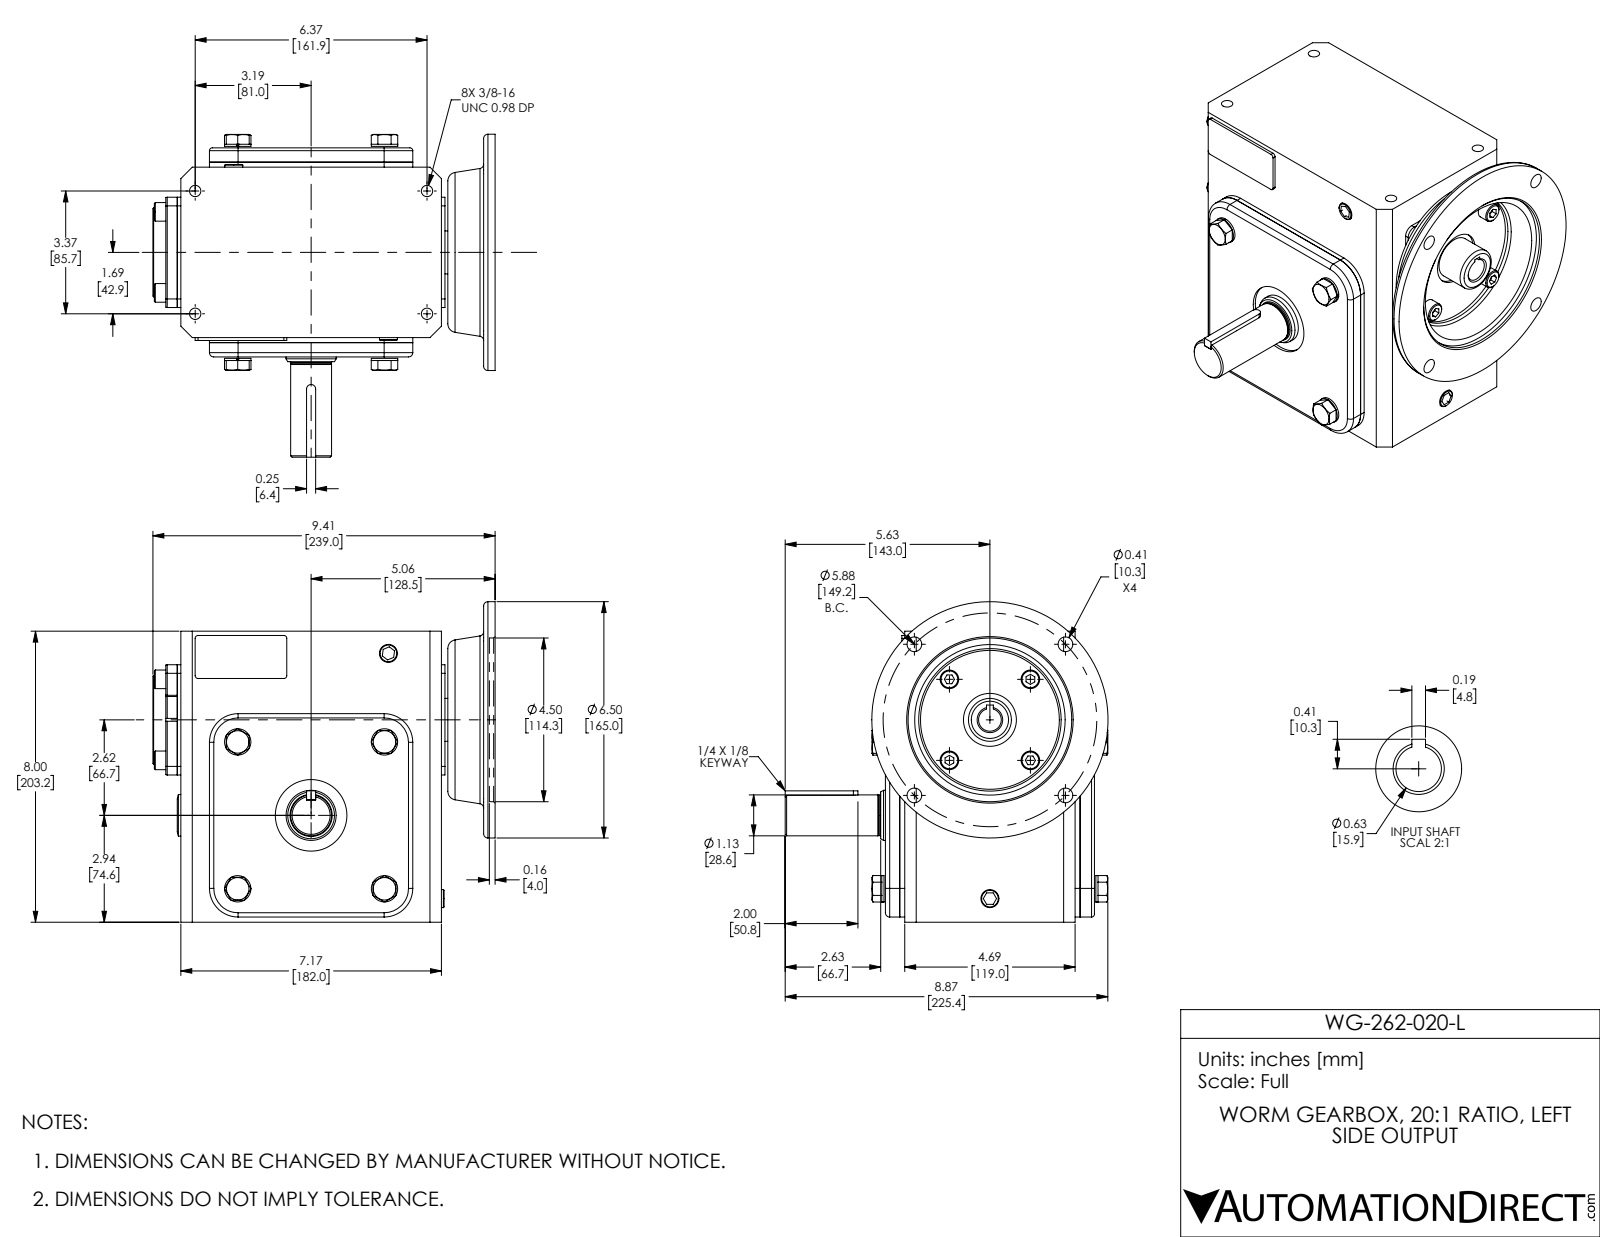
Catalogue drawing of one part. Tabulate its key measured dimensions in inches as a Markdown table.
| quantity | value |
| --- | --- |
| part name | WG-262-020-L |
| STEP written by | SolidWorks 2017 (AUTOMOTIVE_DESIGN) |
| units | inches |
| bodies | 37 solids, 536 faces (293 planar, 145 cylindrical, 98 other) |
| overall size | 9.409 × 8.878 × 8.811 |
| volume | 318.1 in³ |
| surface area | 613.7 in² |
| round holes (diameter × count) | 0.313 × 4, 0.406 × 4, 0.591 × 1, 0.625 × 1, 1.181 × 1, 1.378 × 1, 1.457 × 1, 1.969 × 1, 3.819 × 1, 4.5 × 1 |
| round bosses / shafts (diameter × count) | 0.724 × 4, 0.512 × 4, 6.496 × 1, 2.441 × 1, 2.047 × 1, 1.142 × 1, 1.125 × 1, 1.113 × 1 |
| partial cylindrical surfaces (radius × count) | 0.079 × 12, 0.118 × 4, 0.236 × 4, 0.787 × 4, 0.02 × 2, 0.039 × 2, 0.125 × 1 |
| main face-to-face distances | 0.394, 4.961, 5.354, 0.531, 5.217, 0.138, 4.823, 8, 0.098, 7.264 |
| hole center spacings | 2.937, 4.154, 2.148, 3.375, 5.14, 5.875, 6.375, 7.213 |
